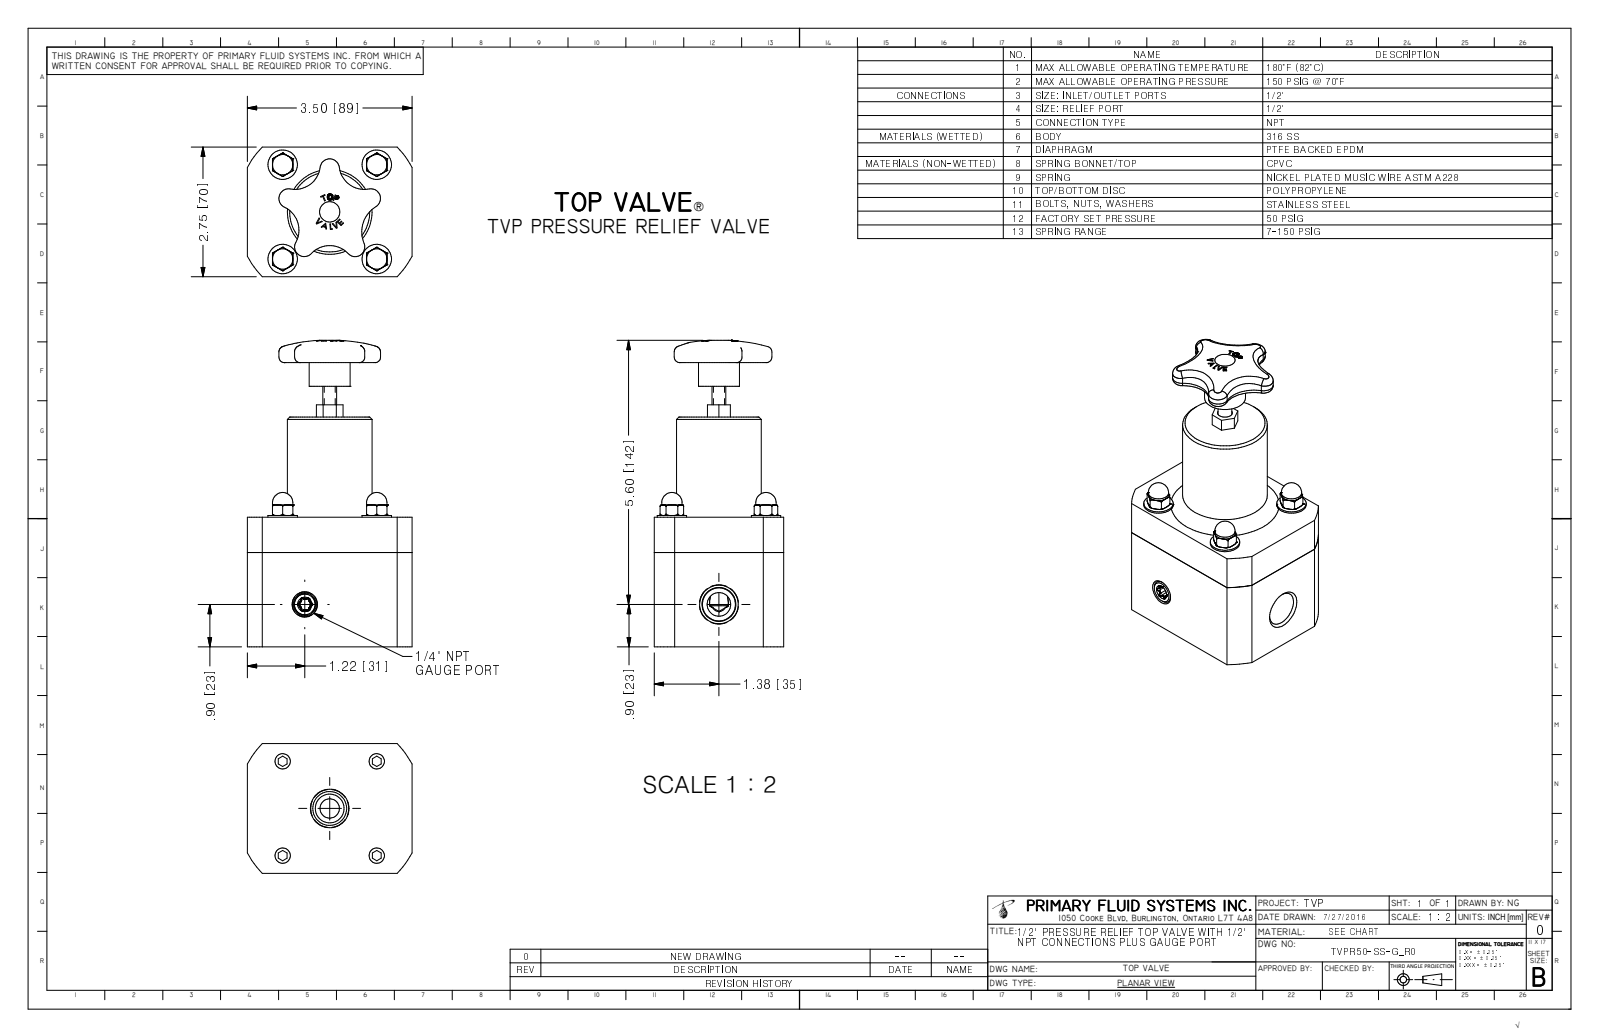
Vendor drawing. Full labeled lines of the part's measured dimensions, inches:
Part name (STEP PRODUCT): TVPR50-SS-G_R0
STEP written by: Autodesk Inventor 2009 (AUTOMOTIVE_DESIGN)
Units: inches
Bodies: 1 solid, 338 faces (131 planar, 50 cylindrical, 157 other)
Overall size (bounding box): 6.5 × 3.5 × 2.75
Volume: 31.93 in³ · Surface area: 81.86 in²
Round holes (diameter × count): ⌀0.175 ×4, ⌀0.719 ×2, ⌀2.4 ×1
Round bosses / shafts (diameter × count): ⌀0.625 ×4, ⌀0.433 ×4, ⌀2.375 ×1, ⌀1.8 ×1, ⌀0.87 ×1, ⌀0.293 ×1
Partial cylindrical surfaces — rounded edges, fillets, slot ends (radius × count): R0.027 ×6, R0.085 ×5, R0.205 ×5, R0.536 ×4, R0.656 ×4, R0.625 ×1, R0.745 ×1, R1.988 ×1
Main face-to-face distances: 2.75, 3.5, 2.75, 4.875, 2.125, 0.7, 2.8, 0.433, 2.786, 0.036
Hole centre spacings: 1.414, 2, 2.828
